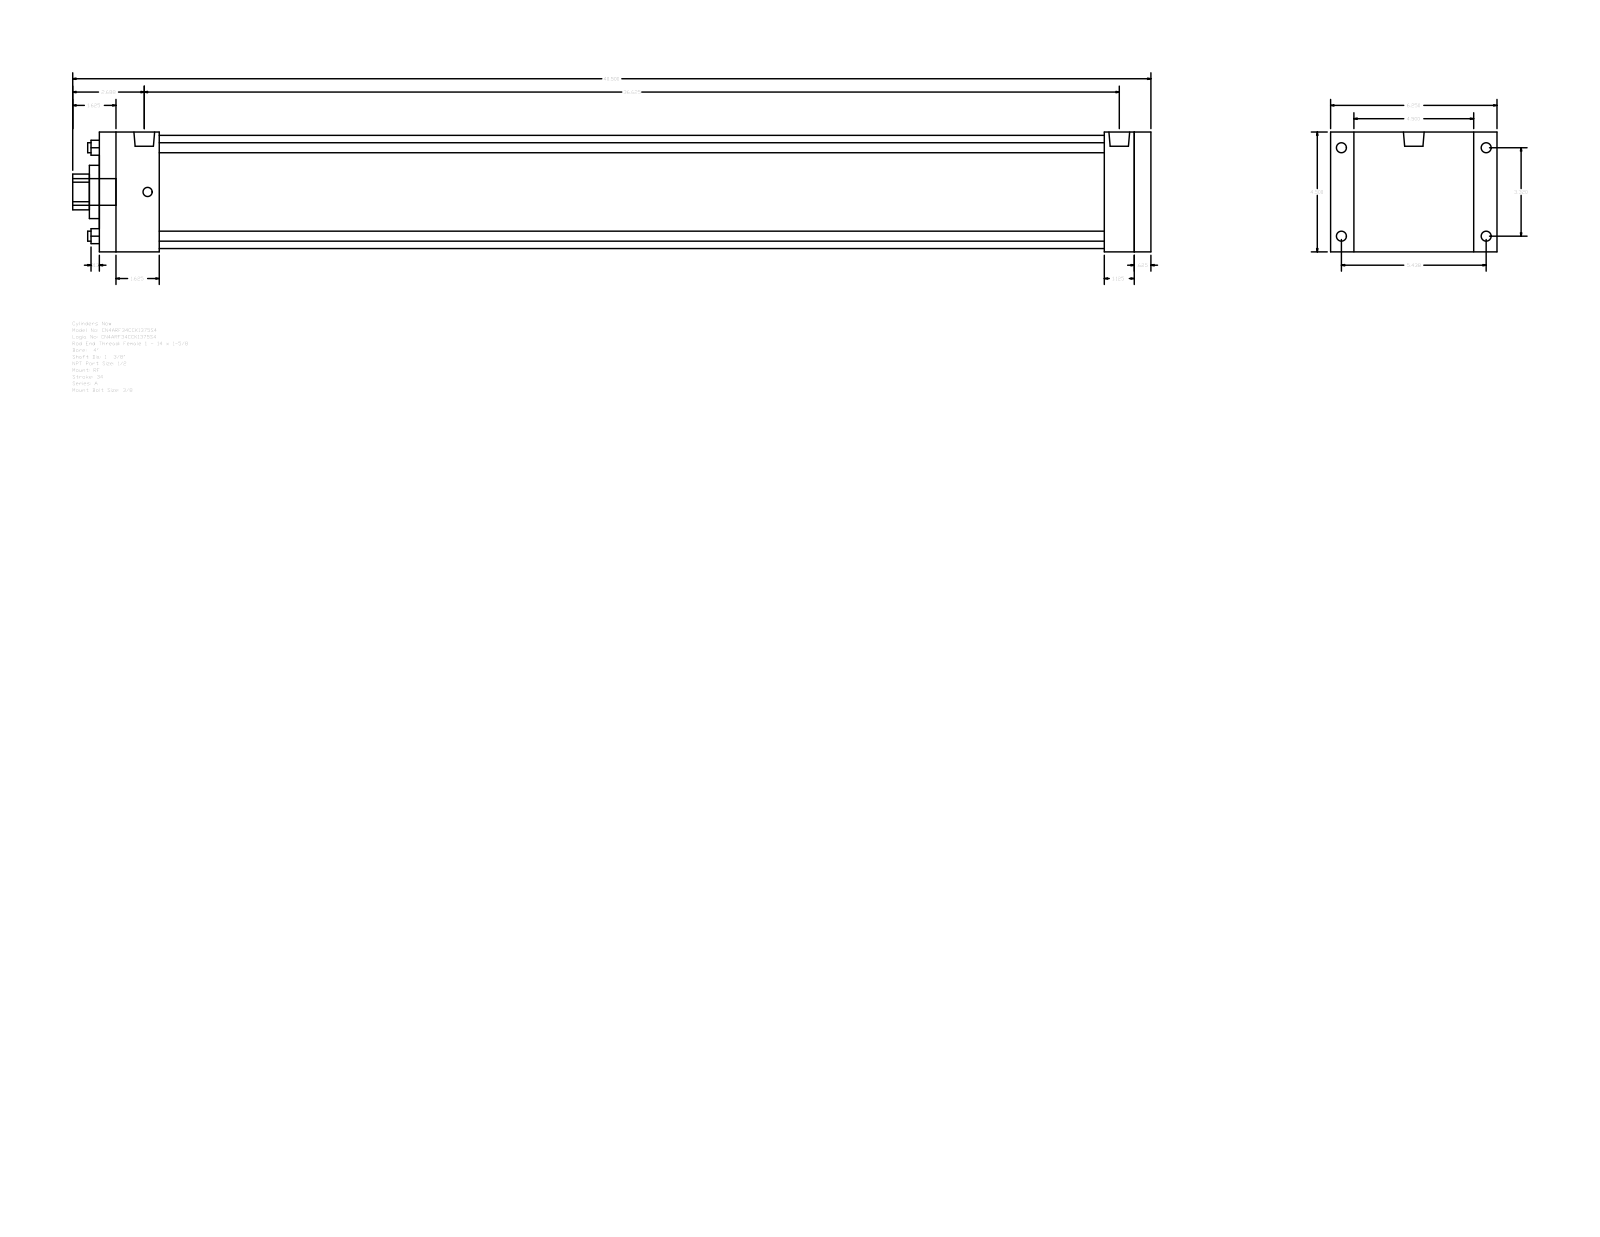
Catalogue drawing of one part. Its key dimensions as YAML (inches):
part_name: "A_RF__0400_1.375"
step_written_by: "GSSL Pune (CONFIG_CONTROL_DESIGN)"
units: inches
bodies: {solids: 0, faces: 92, planar: 64, cylindrical: 28, other: 0}
overall_size: [40.5, 6.25, 4.5]
round_holes:
  - {diameter: 0.375, count: 4}
  - {diameter: 1.375, count: 1}
  - {diameter: 2, count: 1}
  - {diameter: 4.25, count: 1}
round_bosses_or_shafts:
  - {diameter: 0.375, count: 4}
  - {diameter: 0.344, count: 4}
  - {diameter: 0.778, count: 2}
  - {diameter: 1, count: 1}
partial_cylinders:
  - {radius: 0.672, count: 1}
face_to_face_distances: [4.5, 39.5, 0.625, 38.875, 1.125, 0.875, 5.375, 37.75, 1.75, 2.25]
hole_center_spacings: [2.347, 3.32, 4.695]
